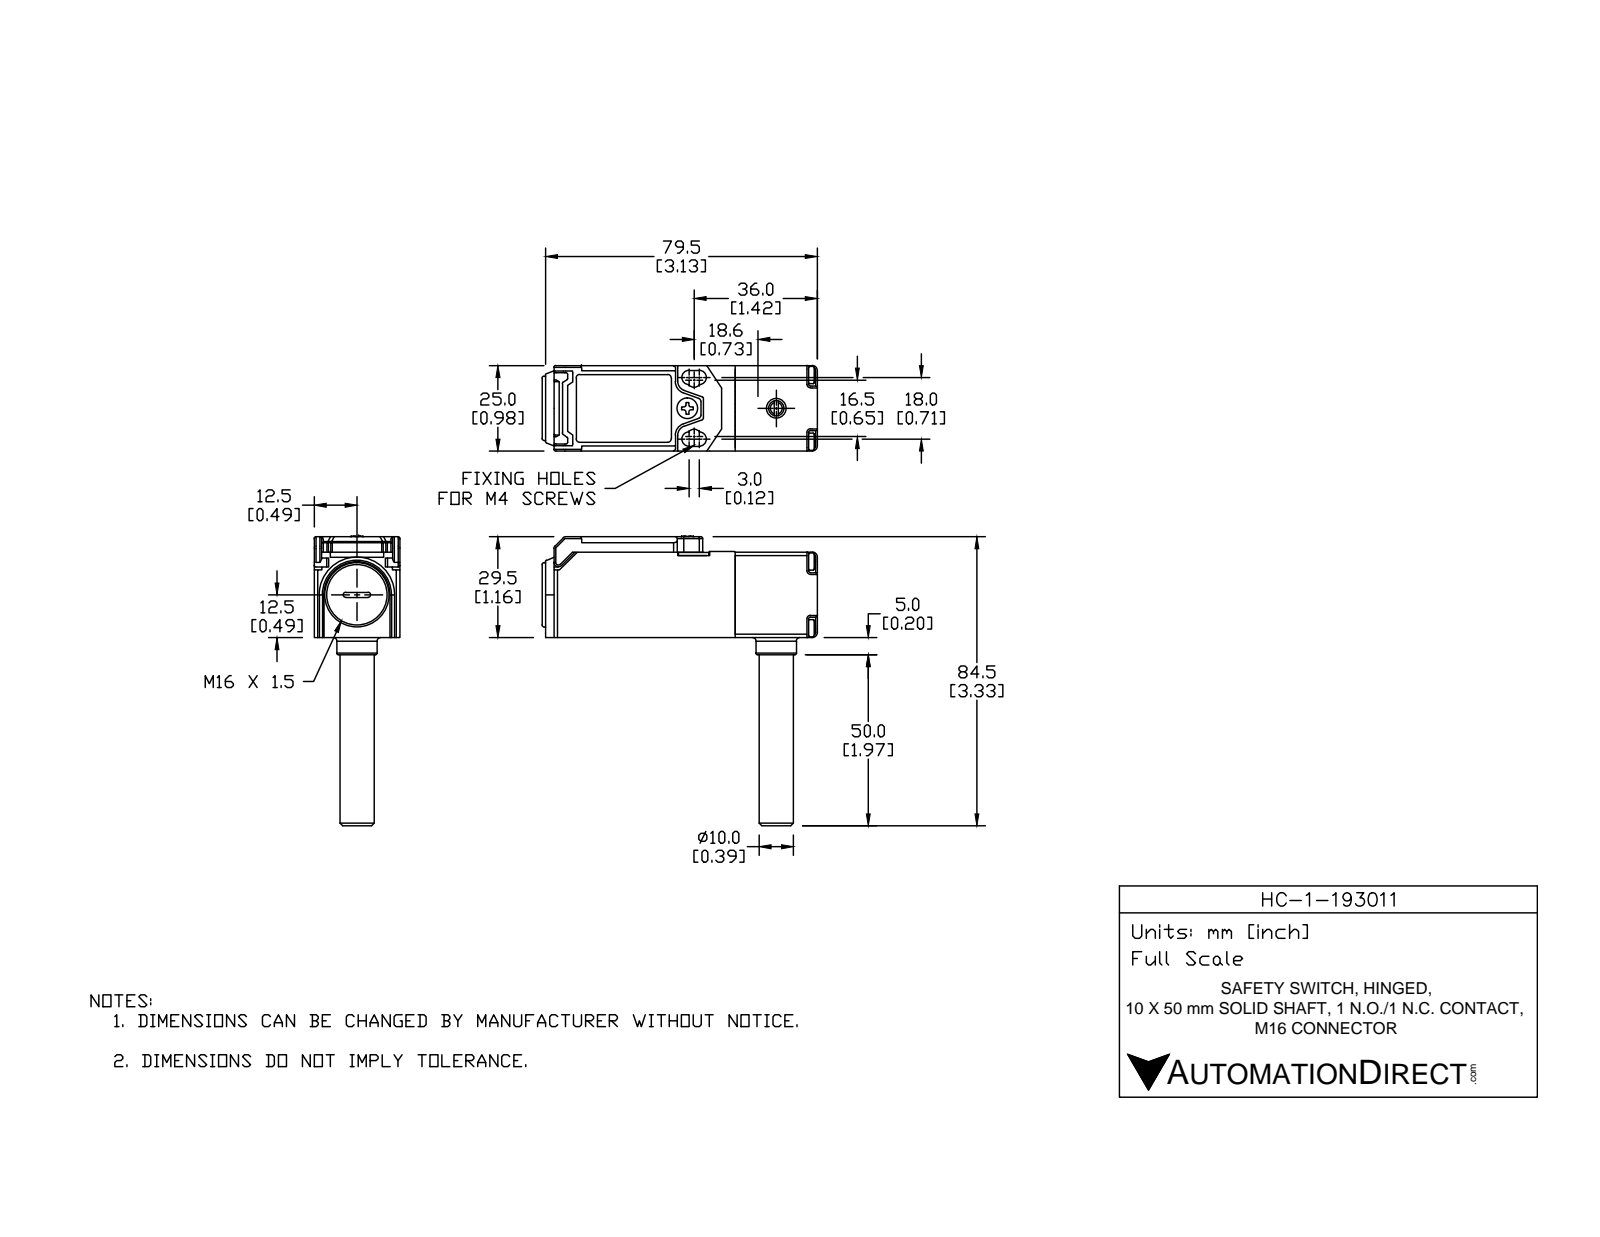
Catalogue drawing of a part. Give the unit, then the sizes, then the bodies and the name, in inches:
Units: inches
Overall size (bounding box): 3.336 × 3.169 × 0.984
Round holes (diameter × count): ⌀0.126 ×5, ⌀0.094 ×4, ⌀0.059 ×2, ⌀0.063 ×2, ⌀0.071 ×2, ⌀0.087 ×2, ⌀0.142 ×2, ⌀0.055 ×1, ⌀0.081 ×1, ⌀0.098 ×1, ⌀0.102 ×1, ⌀0.185 ×1
Round bosses / shafts (diameter × count): ⌀0.102 ×5, ⌀0.197 ×4, ⌀0.079 ×4, ⌀0.138 ×2, ⌀0.74 ×1, ⌀0.531 ×1, ⌀0.394 ×1, ⌀0.386 ×1
Partial cylindrical surfaces — rounded edges, fillets, slot ends (radius × count): R0.02 ×226, R0.004 ×24, R0.012 ×20, R0.039 ×20, R0.059 ×7, R0.083 ×6, R0.11 ×6, R0.008 ×4
Main face-to-face distances: 0.984, 0.079, 0.071, 0.913, 0.039, 0.906, 0.945, 0.827, 0.874, 1.15
Hole centre spacings: 0.543, 0.768, 0.171, 0.187, 0.245, 0.414, 0.423, 0.426
Volume: 1.788 in³ · Surface area: 43.04 in²
Bodies: 14 solids, 1702 faces (700 planar, 601 cylindrical, 401 other)
Part name (STEP PRODUCT): HC-1-193011
STEP written by: SolidWorks 2014 (AUTOMOTIVE_DESIGN)
